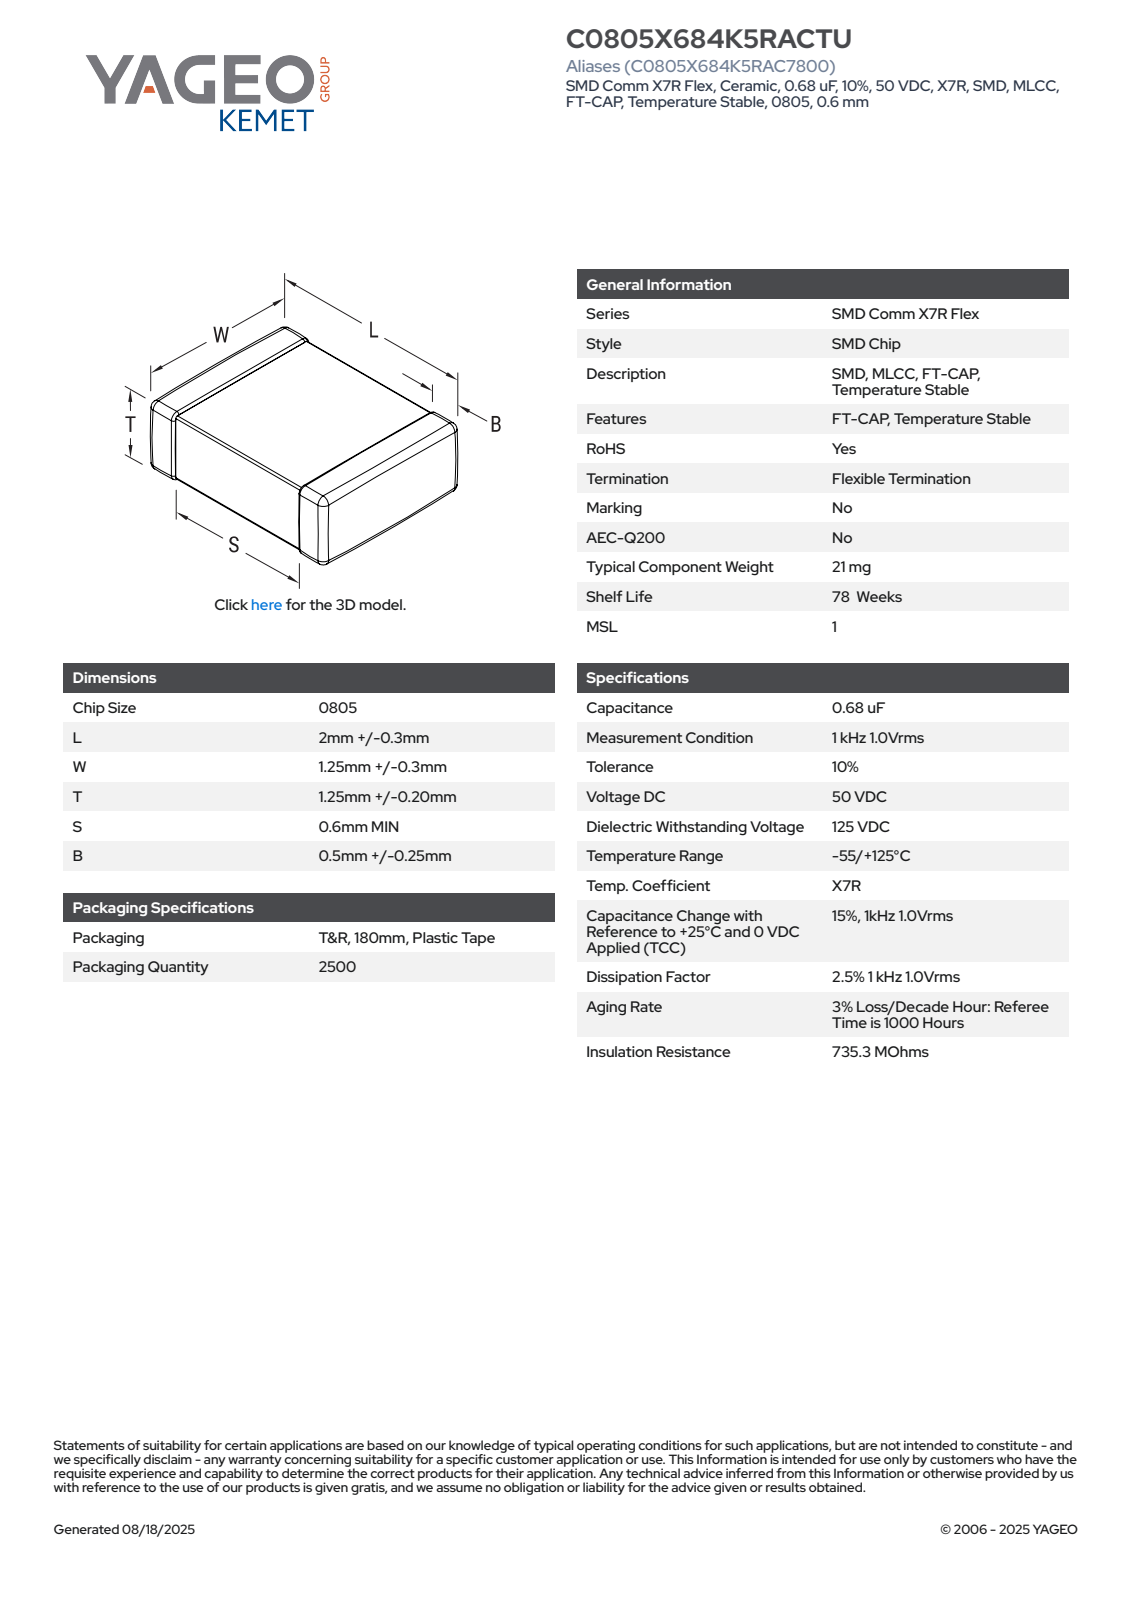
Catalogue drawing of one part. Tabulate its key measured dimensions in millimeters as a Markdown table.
| quantity | value |
| --- | --- |
| part name | CCS_CCSTD_0805_L2.3W1.55T1.45B0.5 |
| STEP written by | SolidWorks 2021 (AUTOMOTIVE_DESIGN) |
| units | millimeters |
| bodies | 4 solids, 125 faces (71 planar, 38 cylindrical, 16 other) |
| overall size | 2.3 × 1.55 × 1.45 |
| volume | 5 mm³ |
| surface area | 18 mm² |
| main face-to-face distances | 1.42, 1.52, 2.3, 1.45, 1.55, 1.39, 1.49, 1.06, 1.24, 1.01 |
